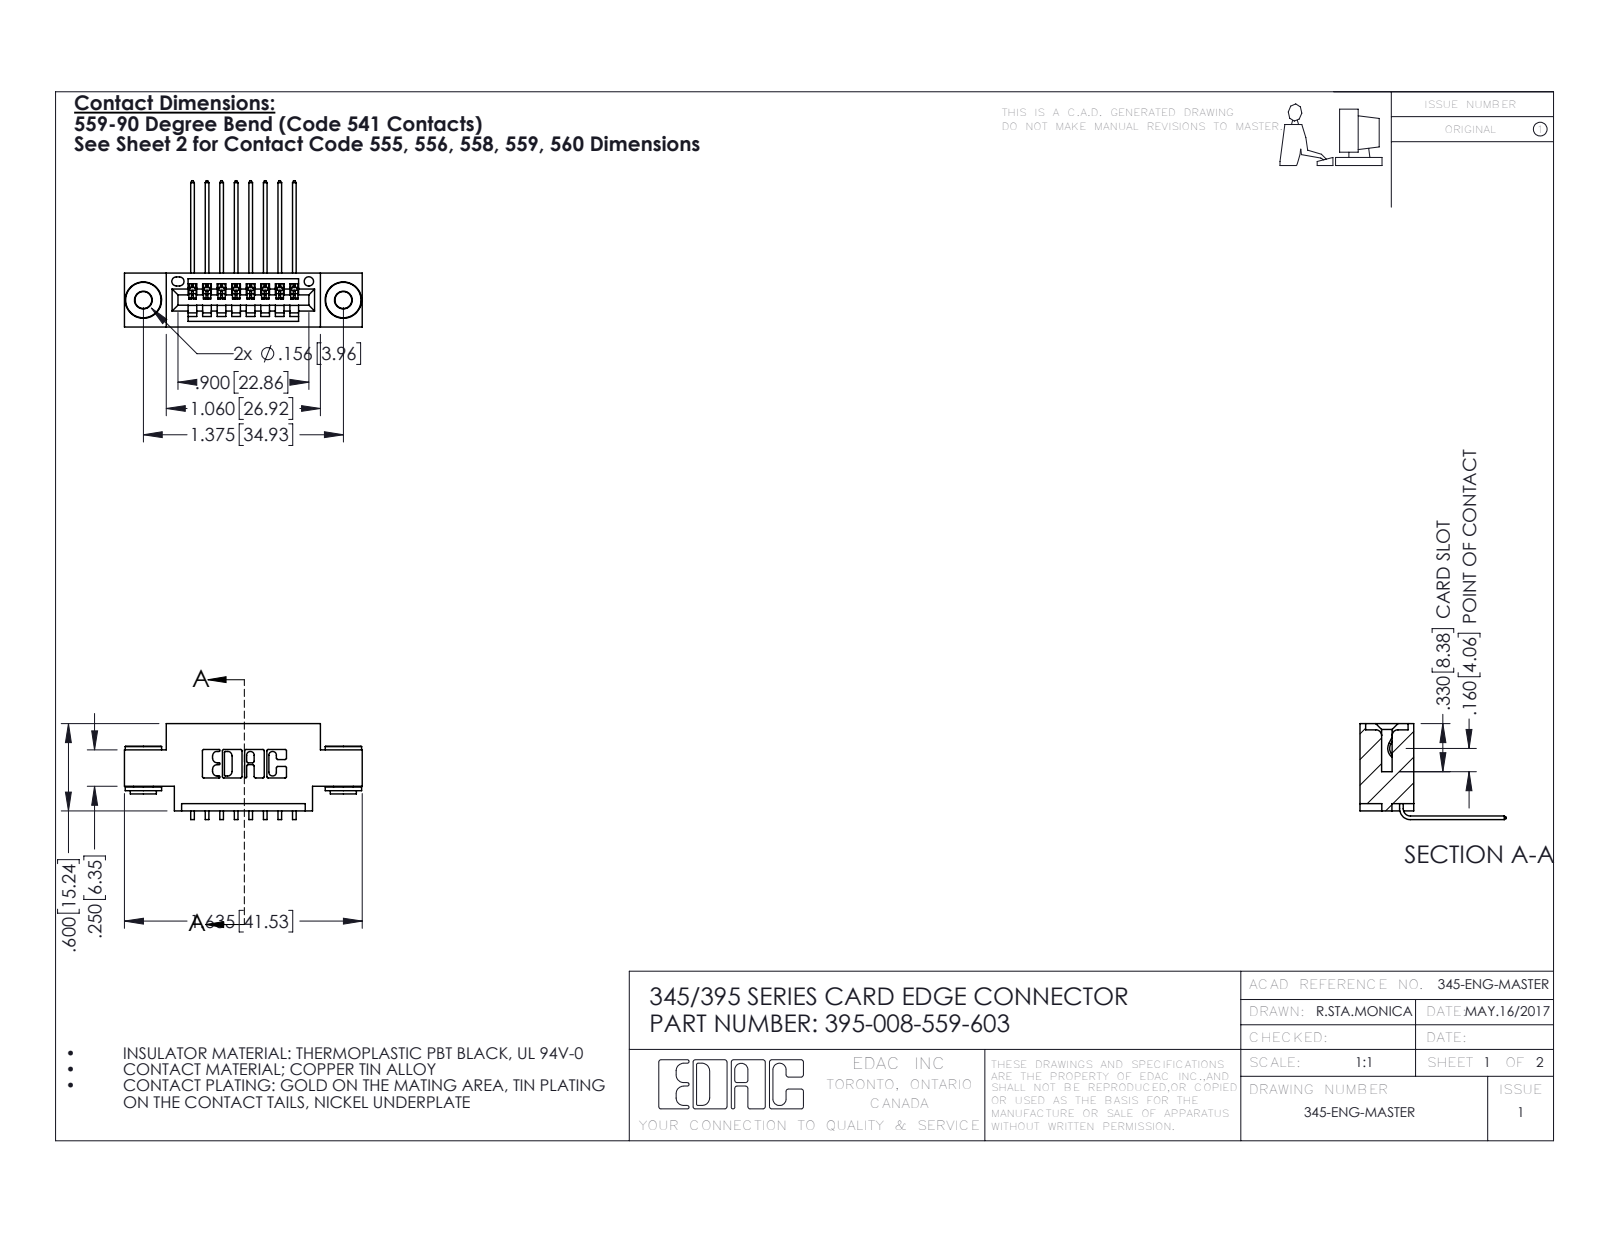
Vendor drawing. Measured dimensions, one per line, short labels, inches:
name: 345-292-001_558 559 Tail - 1; 345-250-002_345-250-002-102; 395-008-559-603; 345 Part_0.170 Offset - 0.156 Dia-TH
written by: SolidWorks 2016 (CONFIG_CONTROL_DESIGN)
unit: in
bodies: 11 solids, 648 faces (430 planar, 210 cylindrical, 8 other)
size: 1.635 × 1.005 × 0.659
volume: 0.22 in³; area: 7.468 in²
holes: 2× ⌀0.116, 2× ⌀0.156, 1× ⌀0.064
bosses: 2× ⌀0.25, 2× ⌀0.18, 2× ⌀0.136
rounds: 22× R0.01, 16× R0.006, 6× R0.007, 6× R0.031, 3× R0.026, 2× R0.031, 2× R0.04, 1× R0.014
face distances: 0.37, 0.2, 0.072, 0.298, 0.1, 0.098, 0.272, 0.025, 0.06, 0.25
hole spacings: 0.27, 1.144, 1.375
